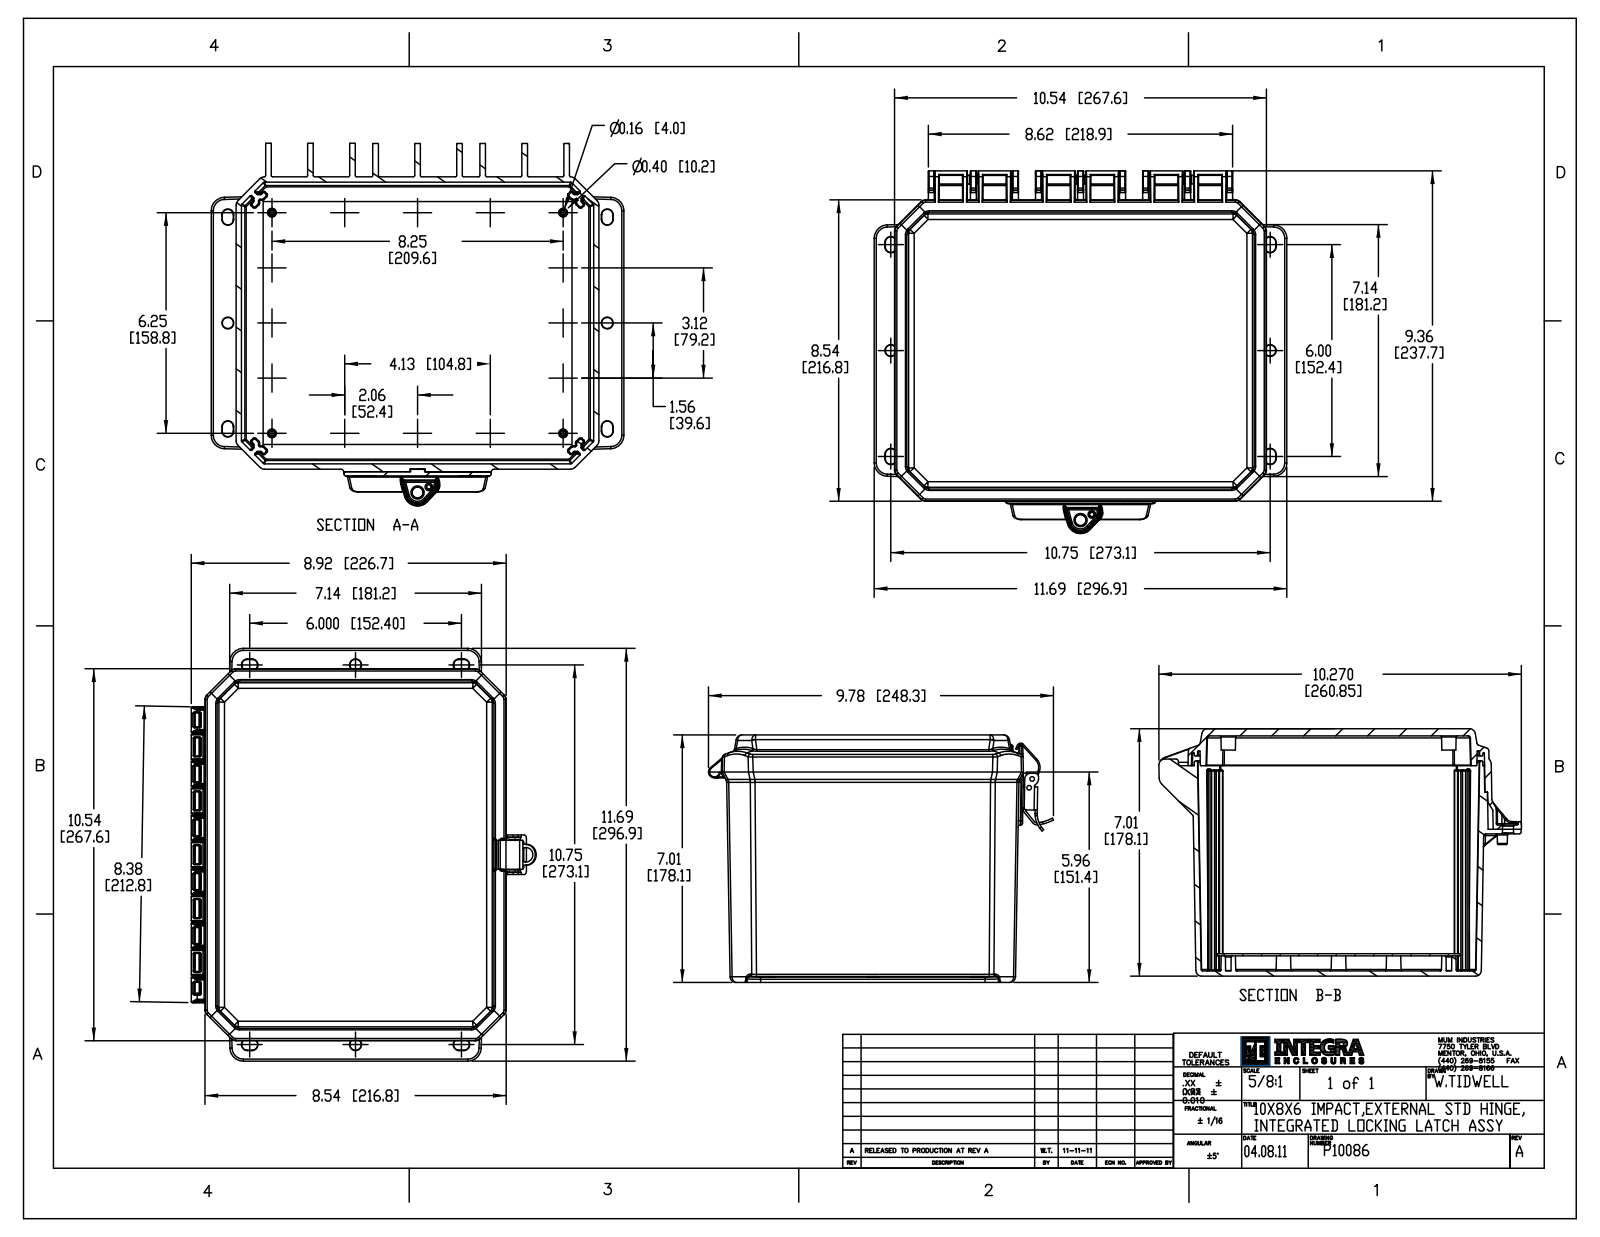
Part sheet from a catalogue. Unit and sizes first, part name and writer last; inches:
Units: inches
Overall size (bounding box): 11.69 × 10.271 × 7.01
Round holes (diameter × count): ⌀0.12 ×1
Round bosses / shafts (diameter × count): ⌀0.242 ×1
Partial cylindrical surfaces — rounded edges, fillets, slot ends (radius × count): R0.02 ×101, R0.015 ×90, R0.04 ×83, R0.03 ×77, R0.06 ×50, R0.01 ×49, R0.029 ×44, R0.15 ×16
Main face-to-face distances: 0.15, 7.01, 6.86, 6.805, 6.655, 0.205, 1.05, 5.96, 5.81, 0.845
Volume: 75.14 in³ · Surface area: 962.6 in²
Bodies: 2 solids, 2464 faces (642 planar, 811 cylindrical, 1011 other)
Part name (STEP PRODUCT): P1086BH; P108CHO; P10086_ASM
STEP written by: PRO/ENGINEER BY PARAMETRIC TECHNOLOGY CORPORATION, 2011190 (CONFIG_CONTROL_DESIGN)
